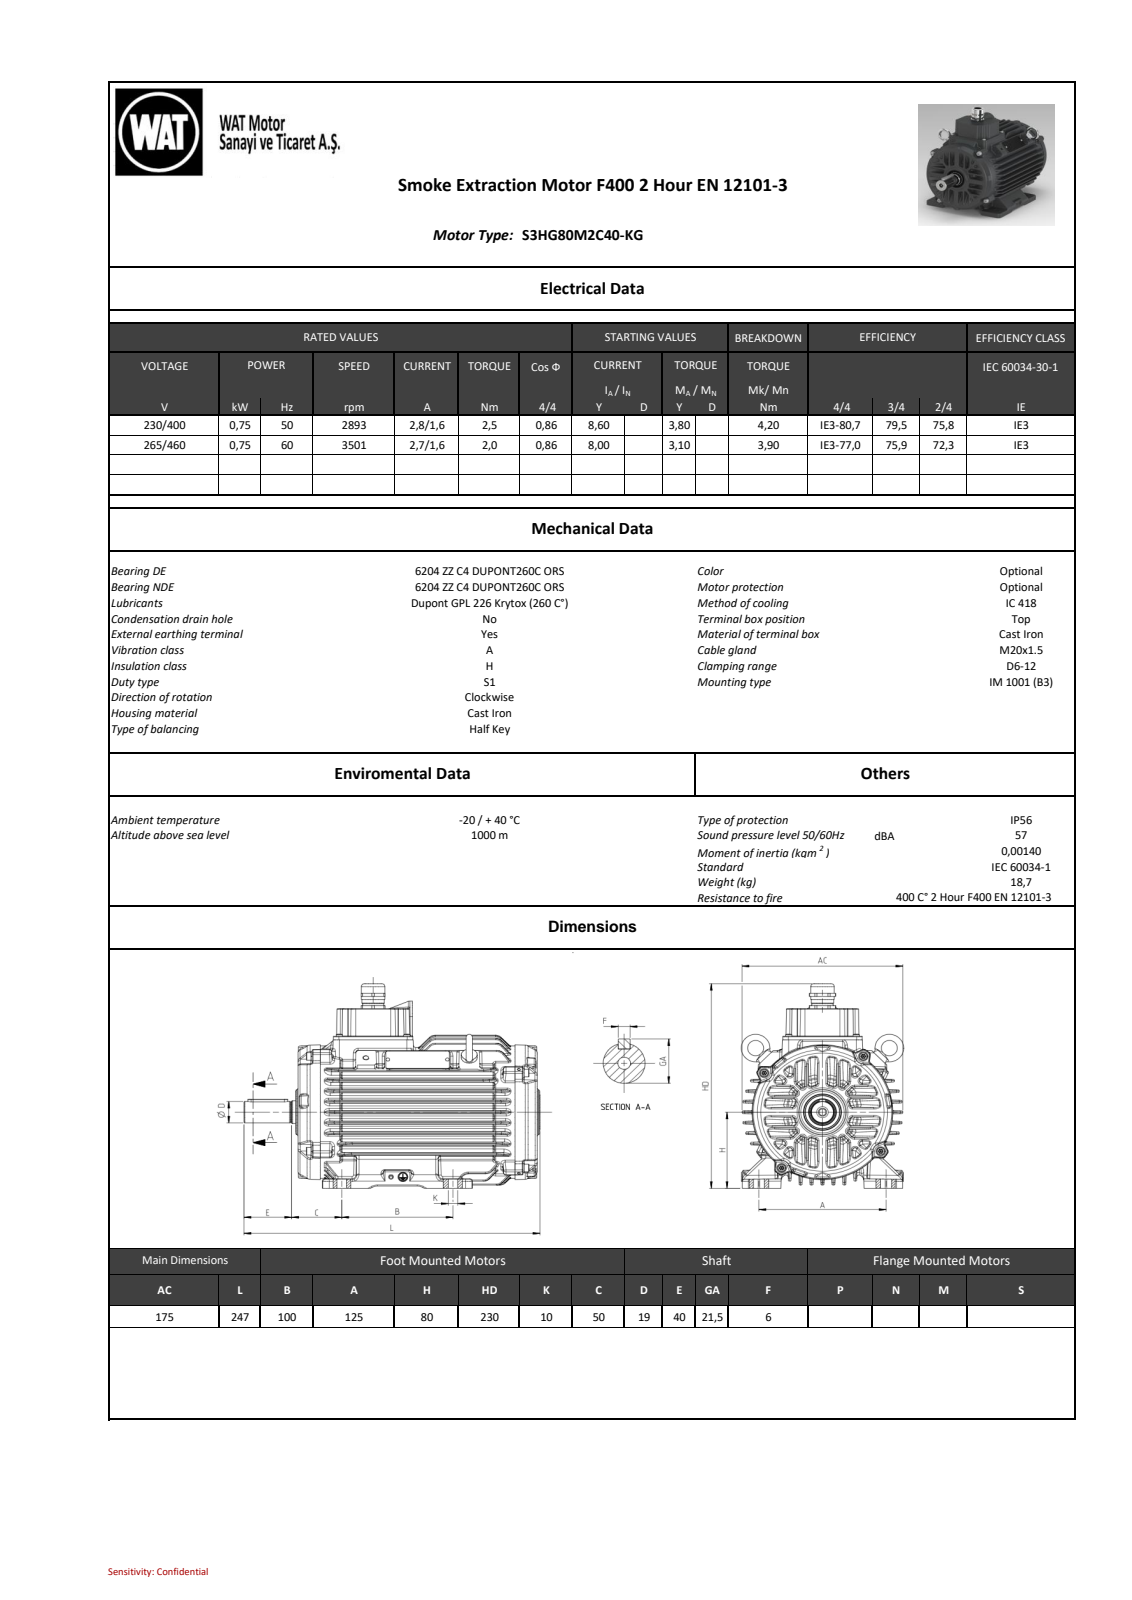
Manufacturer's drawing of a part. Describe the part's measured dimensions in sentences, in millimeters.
The part is named "26032C0836B7xhp9". Its 3-D file was written by "SIEMENS PLM Software NX 11.0 (AUTOMOTIVE_DESIGN)". It is 0 solids with 2988 faces: 578 planar, 752 cylindrical and 1658 other. Overall it measures 247.2 by 230.06 by 221.33 millimeters. Round holes: 5 of diameter 3.3, 2 of diameter 2.5, 1 of diameter 6.4, 1 of diameter 14, 1 of diameter 24, 1 of diameter 27.8, 1 of diameter 28, 1 of diameter 32. Round bosses or shafts: 4 of diameter 8, 3 of diameter 20, 3 of diameter 9.2, 3 of diameter 8.28, 3 of diameter 5, 1 of diameter 23.7, 1 of diameter 22.4, 1 of diameter 21.06. Partial cylindrical surfaces (rounded edges, fillets, slot ends): 399 of radius 1.5, 50 of radius 2, 46 of radius 2.5, 19 of radius 0.5, 17 of radius 1, 16 of radius 4, 10 of radius 5, 6 of radius 12. The main face-to-face distances are 192.83, 39.97, 152.96, 192.93, 197.83, 5, 0.8, 0.77, 18.33, 174.5. The hole center spacings are 75.
